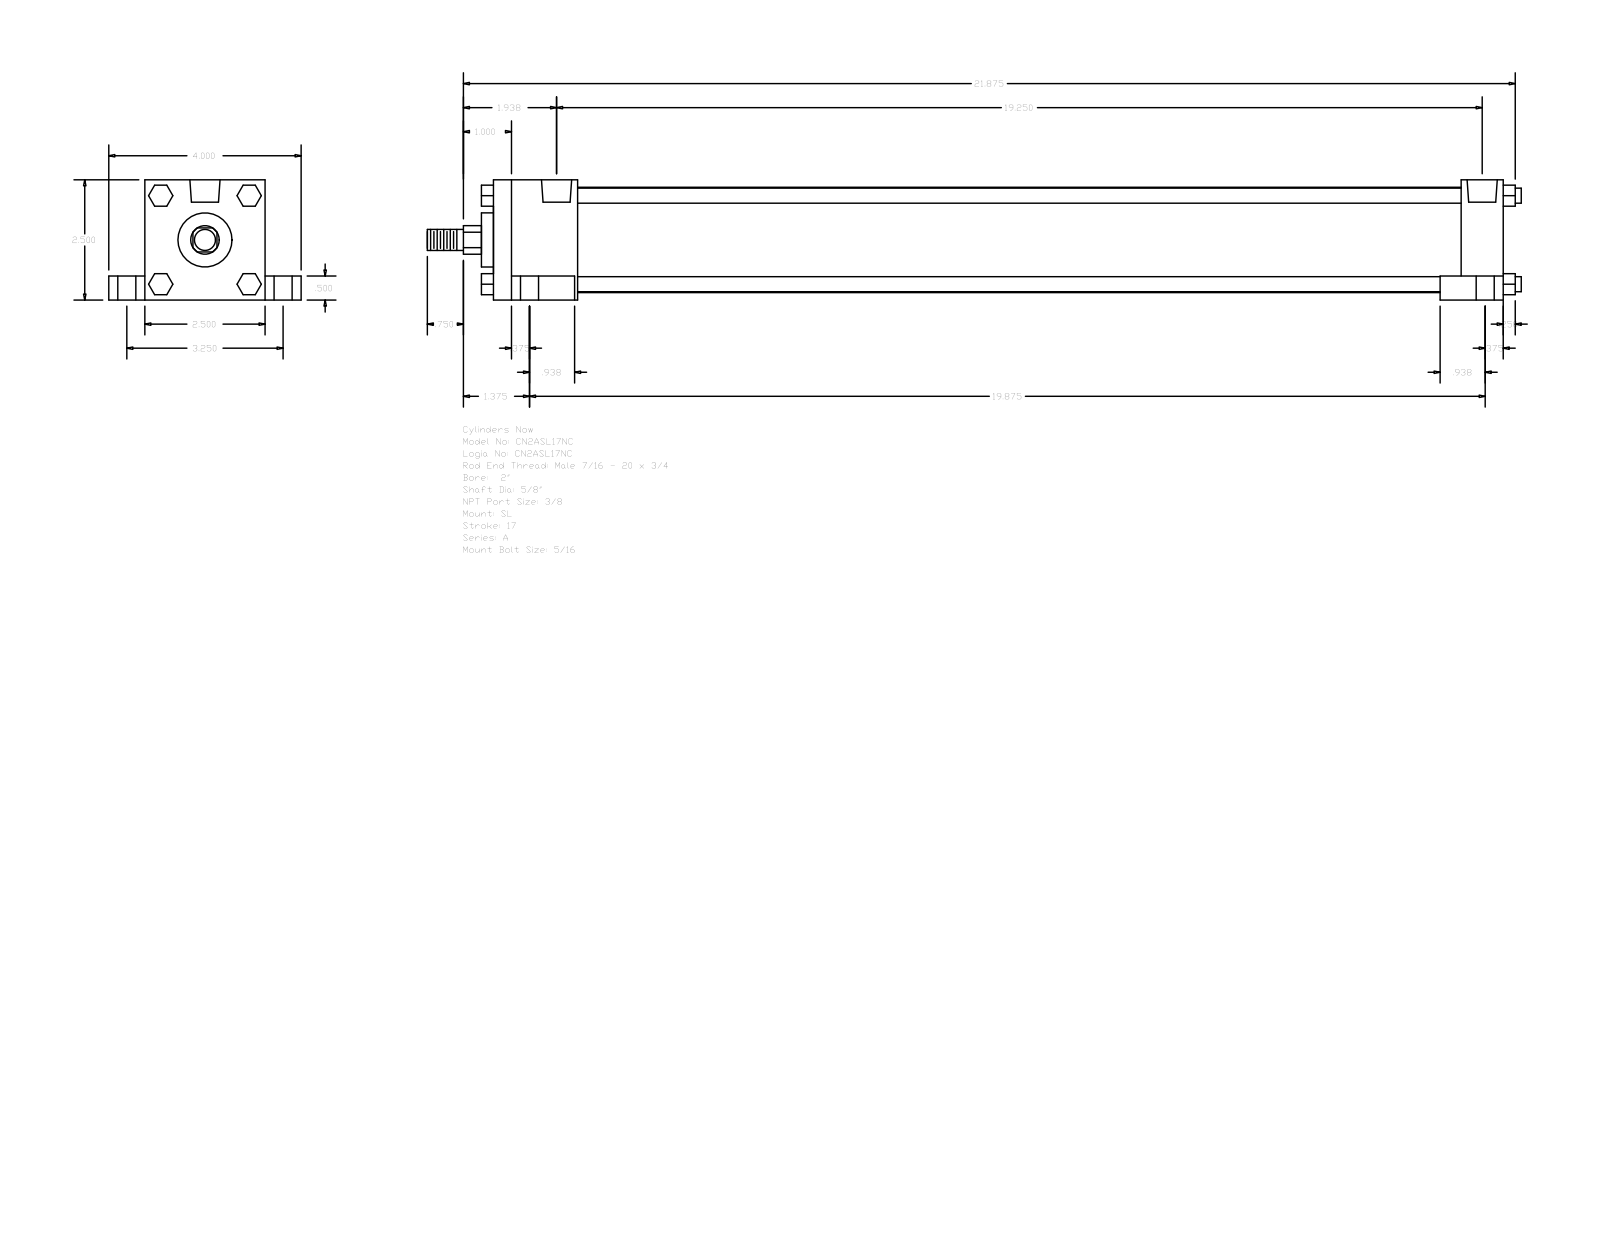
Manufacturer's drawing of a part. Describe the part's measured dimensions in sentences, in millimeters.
The part is named "A_SL__0200_0.625". Its 3-D file was written by "GSSL Pune (CONFIG_CONTROL_DESIGN)". It is 0 solids with 148 faces: 112 planar, 36 cylindrical and 0 other. Overall it measures 577.85 by 101.6 by 63.5 millimeters. Round holes: 4 of diameter 5.56, 4 of diameter 9.53, 4 of diameter 15.88, 2 of diameter 15.93. Round bosses or shafts: 4 of diameter 7.94, 1 of diameter 55.63, 1 of diameter 28.57, 1 of diameter 15.88, 1 of diameter 11.11. Partial cylindrical surfaces (rounded edges, fillets, slot ends): 1 of radius 7.54. The main face-to-face distances are 63.5, 533.39, 50.8, 12.7, 19.05, 82.55, 44.45, 488.94, 511.17, 466.72. The hole center spacings are 41.3, 41.64, 43.67, 45.13, 82.54, 481, 488.31, 492.27.
